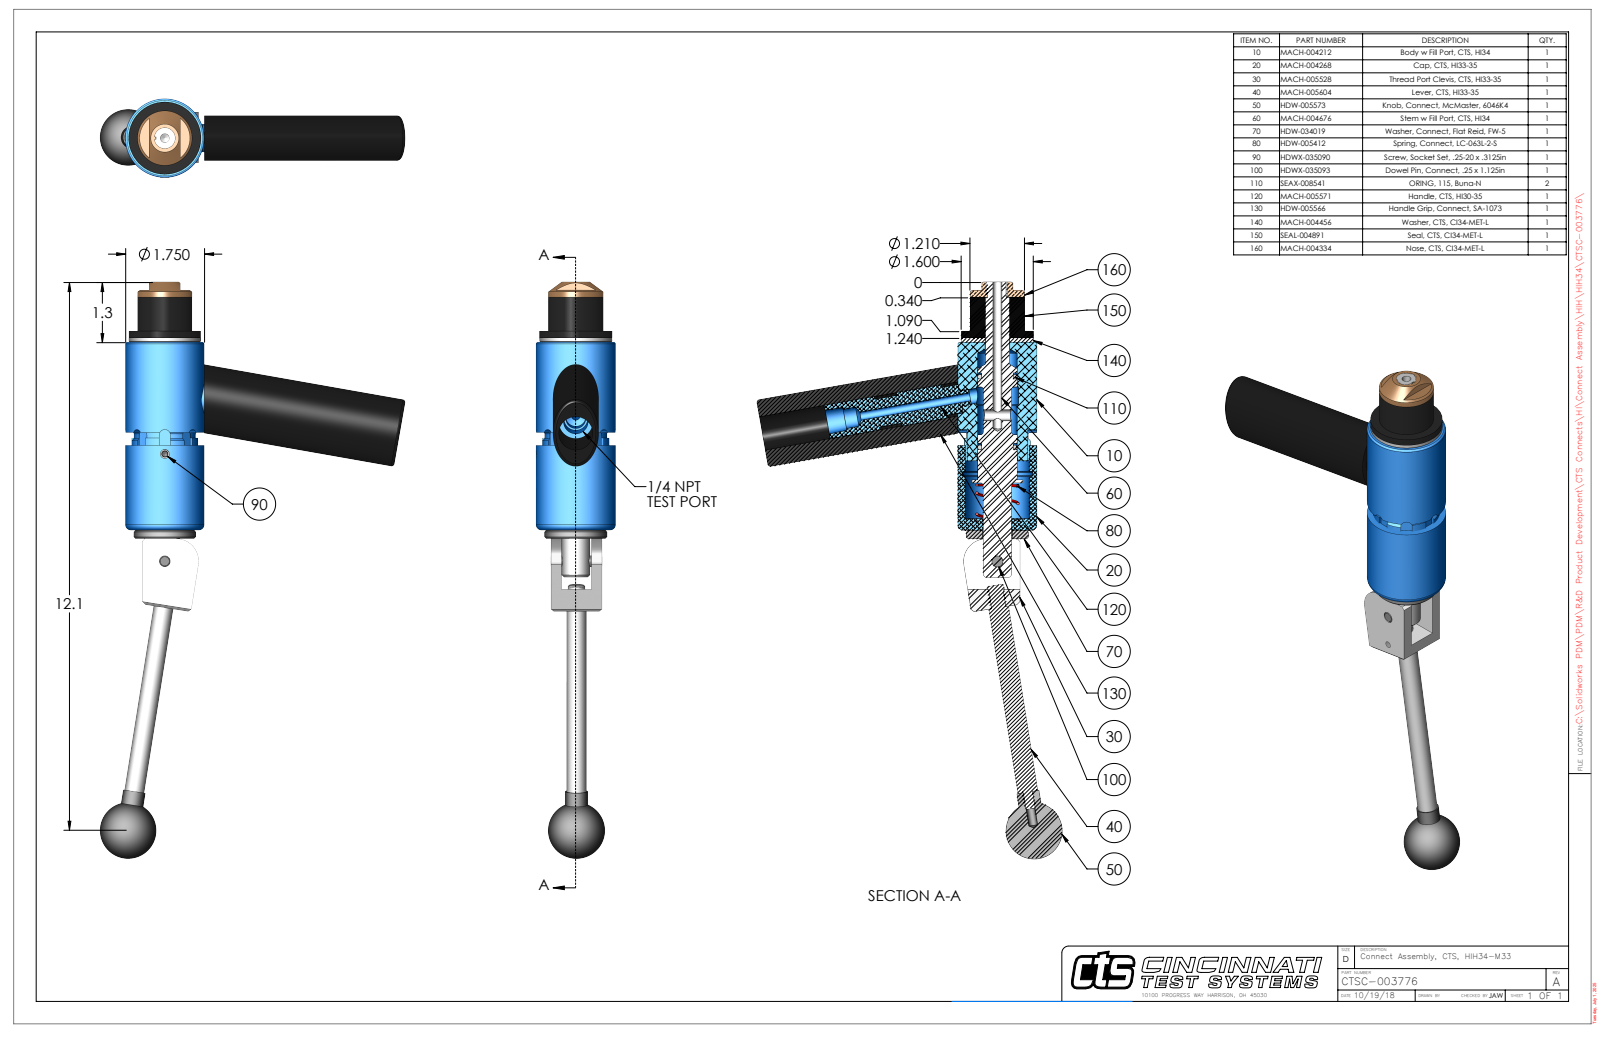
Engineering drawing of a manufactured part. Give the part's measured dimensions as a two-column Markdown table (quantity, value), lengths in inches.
| quantity | value |
| --- | --- |
| part name | CTSC-003776 |
| STEP written by | SolidWorks 2023 (AUTOMOTIVE_DESIGN) |
| units | inches |
| bodies | 10 solids, 341 faces (123 planar, 143 cylindrical, 75 other) |
| overall size | 12.773 × 6.763 × 1.75 |
| volume | 18.89 in³ |
| surface area | 119.7 in² |
| round holes (diameter × count) | 0.201 × 2, 0.15 × 1, 0.187 × 1, 0.204 × 1, 0.249 × 1, 0.25 × 1, 0.251 × 1, 0.313 × 1, 0.422 × 1, 0.438 × 1, 0.53 × 1, 0.541 × 1 |
| round bosses / shafts (diameter × count) | 0.5 × 2, 0.44 × 2, 0.25 × 2, 1.75 × 1, 1.6 × 1, 1.38 × 1, 1.21 × 1, 0.75 × 1 |
| partial cylindrical surfaces (radius × count) | 0.125 × 4, 0.029 × 2, 0.166 × 1, 0.166 × 1, 0.182 × 1, 0.33 × 1, 0.5 × 1, 0.695 × 1 |
| main face-to-face distances | 0.094, 4.258, 4.164, 0.9, 0.994, 5.158, 1.12, 5.346, 4.446, 4.352 |
| hole center spacings | 0.74, 2.376, 3.116 |
